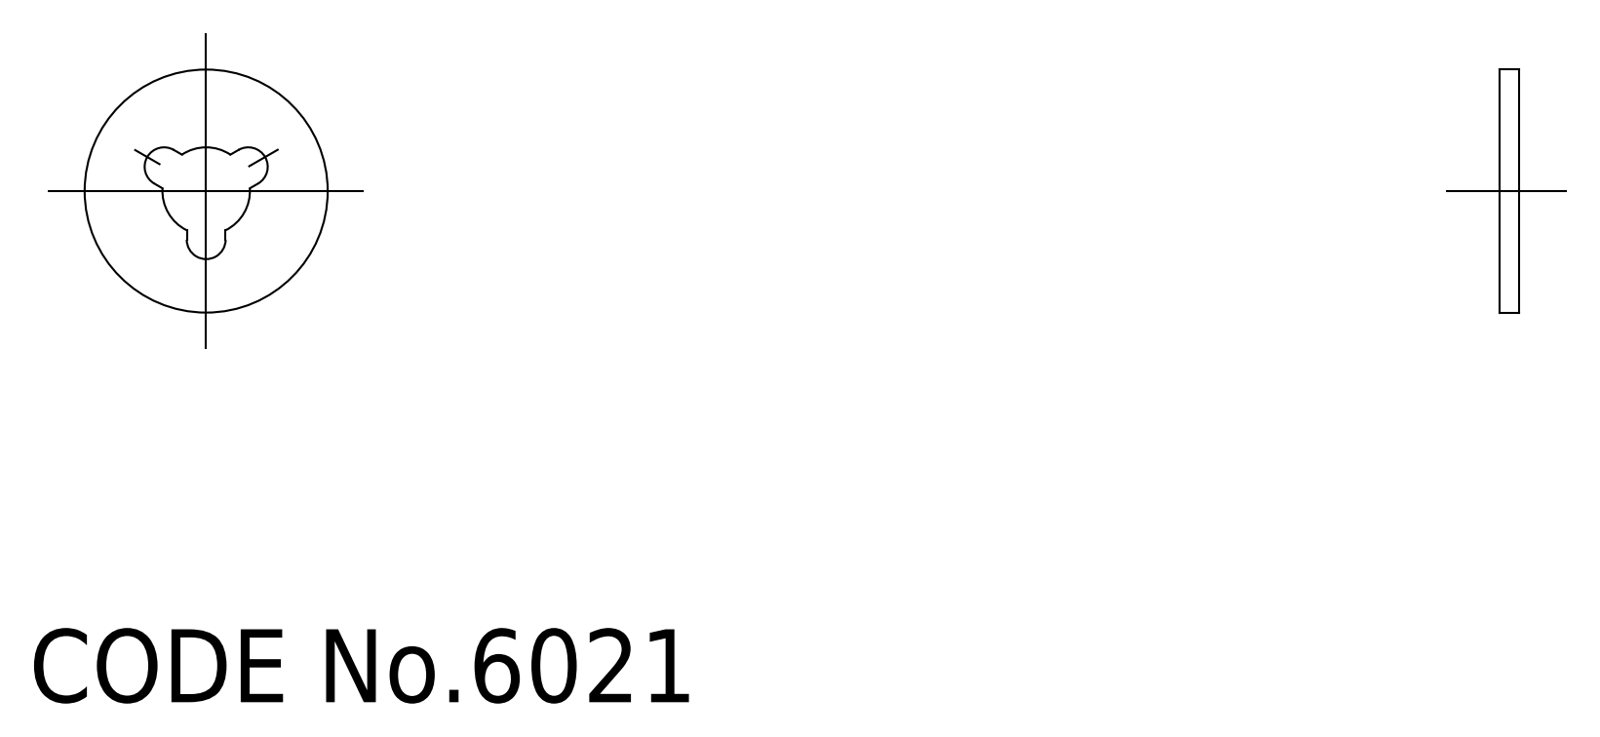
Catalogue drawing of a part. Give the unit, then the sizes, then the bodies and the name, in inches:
Units: inches
Overall size (bounding box): 0.394 × 0.394 × 0.031
Volume: 0.003 in³ · Surface area: 0.257 in²
Bodies: 1 solid, 16 faces (0 planar, 0 cylindrical, 16 other)
Part name (STEP PRODUCT): washer
STEP written by: CADfix (AUTOMOTIVE_DESIGN)
